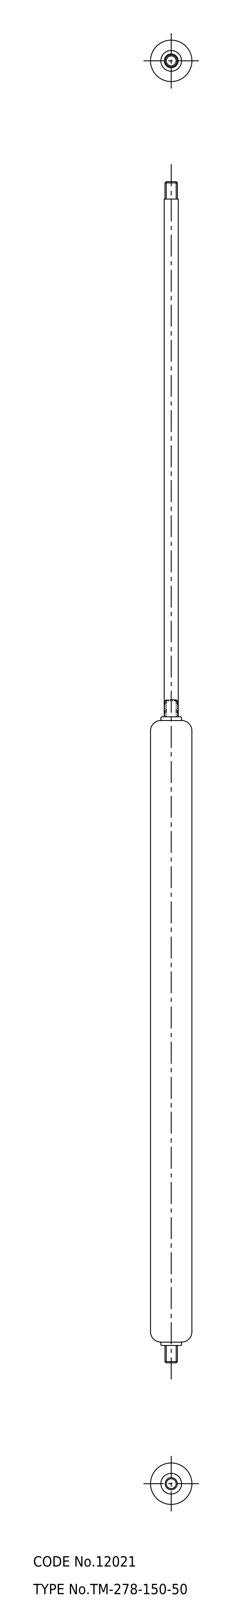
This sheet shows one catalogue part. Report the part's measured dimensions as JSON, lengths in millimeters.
{"part_name": "rod; TM_278_150_50_30126_36", "step_written_by": "CADfix (AUTOMOTIVE_DESIGN)", "units": "millimeters", "bodies": {"solids": 2, "faces": 36, "planar": 0, "cylindrical": 0, "other": 36}, "overall_size": [342, 12, 12], "volume_mm3": 22311, "surface_area_mm2": 9000}
